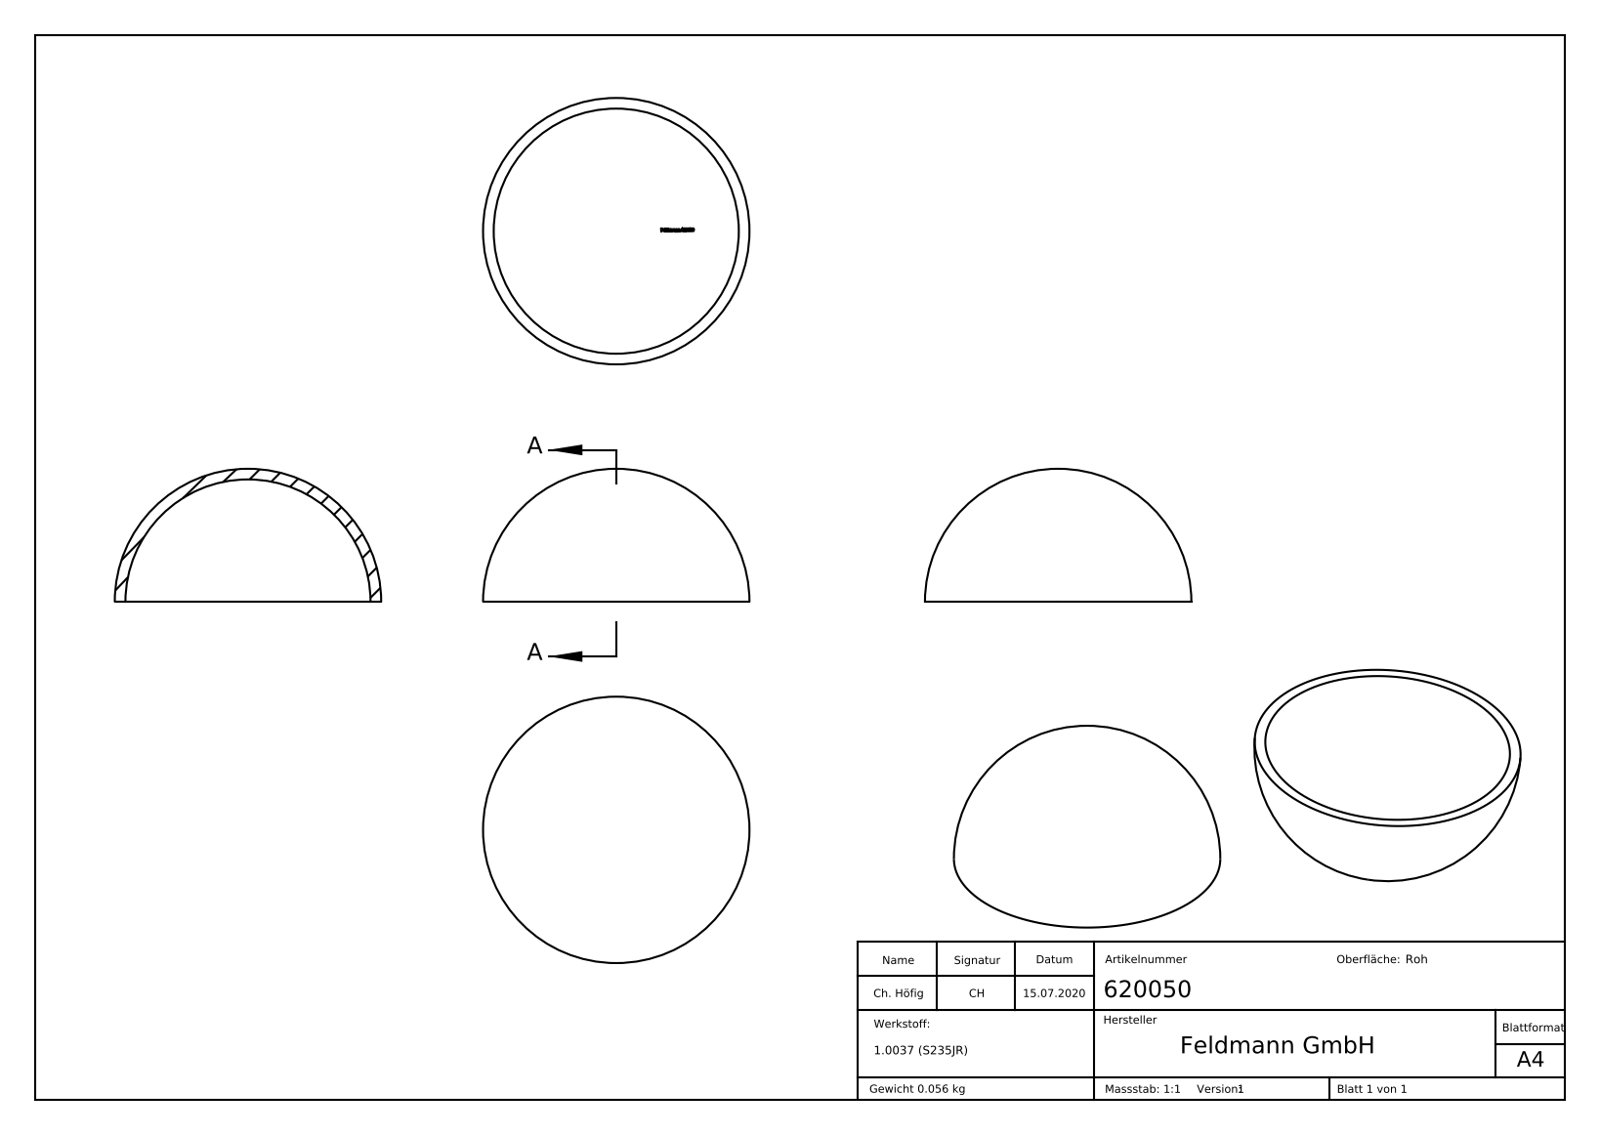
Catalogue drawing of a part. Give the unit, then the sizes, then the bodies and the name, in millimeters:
Units: millimetres
Overall size (bounding box): 50 × 50 × 25
Main face-to-face distances: 1.19, 0.55, 0.5, 0.53, 0.81, 0.45, 0.66, 1.74, 1.31, 0.4
Volume: 7 242 mm³ · Surface area: 7 556 mm²
Bodies: 1 solid, 191 faces (70 planar, 0 cylindrical, 121 other)
Part name (STEP PRODUCT): 620050
STEP written by: SolidWorks 2018 (CONFIG_CONTROL_DESIGN)
